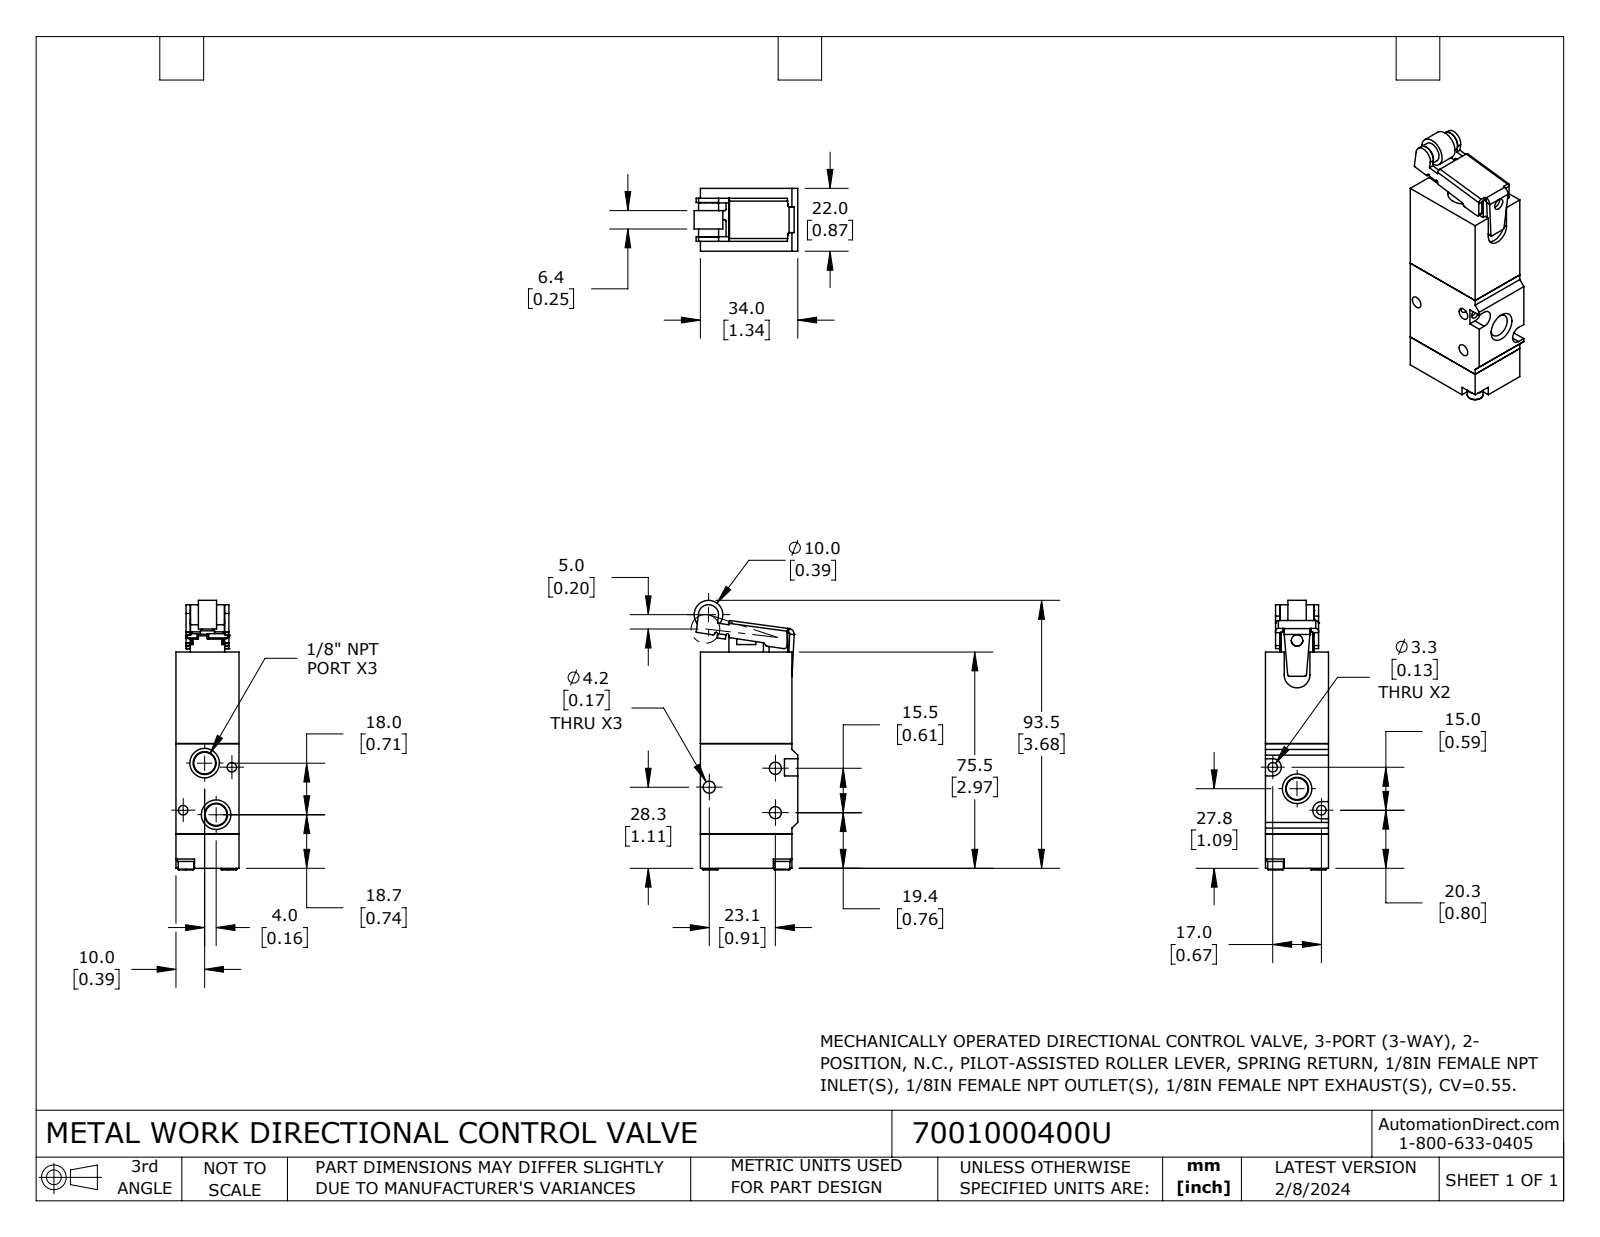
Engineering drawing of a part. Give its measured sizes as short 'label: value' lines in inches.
name: 7001000400U
written by: SolidWorks 2023 (CONFIG_CONTROL_DESIGN)
unit: in
bodies: 8 solids, 277 faces (138 planar, 95 cylindrical, 44 other)
size: 3.705 × 1.423 × 0.866
volume: 3.333 in³; area: 27.9 in²
holes: 3× ⌀0.165, 2× ⌀0.118, 2× ⌀0.13, 1× ⌀0.157
bosses: 2× ⌀0.236, 2× ⌀0.217, 1× ⌀0.472, 1× ⌀0.394, 1× ⌀0.276, 1× ⌀0.197, 1× ⌀0.12, 1× ⌀0.118
rounds: 15× R0.02, 4× R0.004, 4× R0.039, 2× R0.059, 2× R0.118, 1× R0.079, 1× R0.177
face distances: 0.866, 1.26, 1.24, 0.059, 0.472, 1.713, 0.138, 2.972, 2.5, 0.079
hole spacings: 0.61, 0.893, 0.946, 0.975, 1.148
